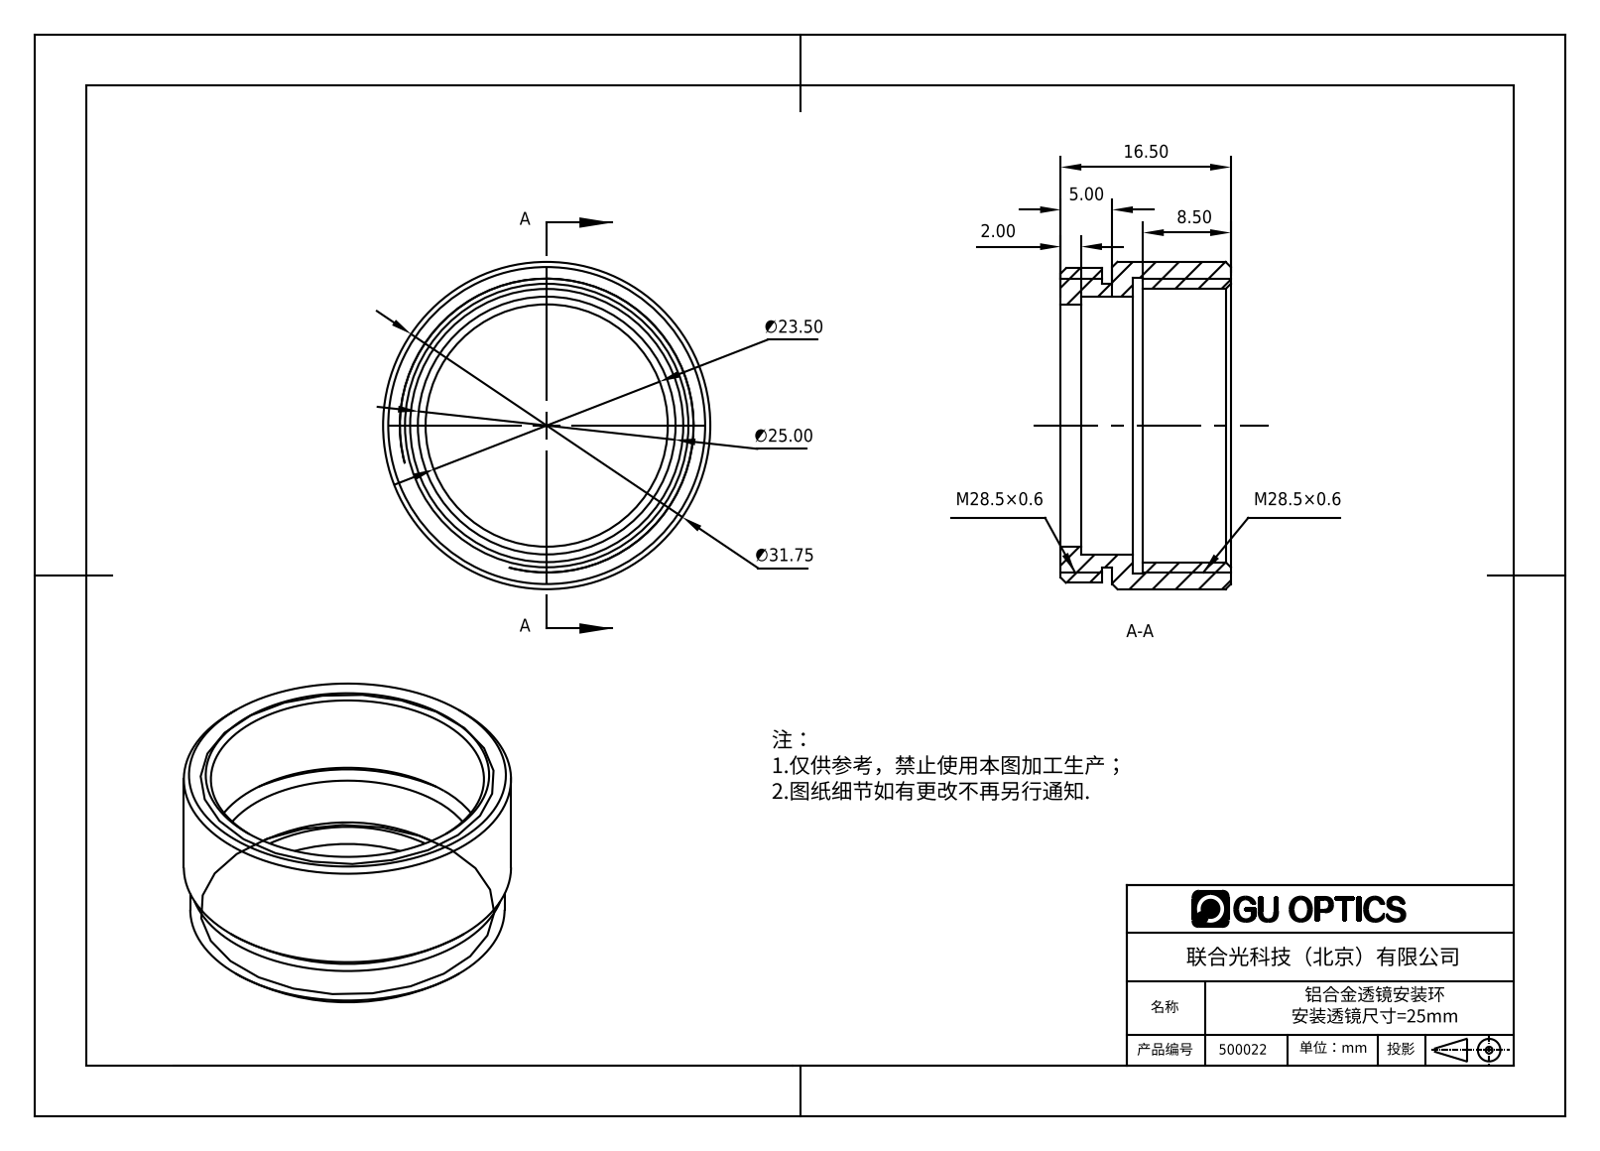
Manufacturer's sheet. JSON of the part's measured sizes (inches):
{"part_name": "500022", "step_written_by": "SolidWorks 2016 (AUTOMOTIVE_DESIGN)", "units": "inches", "bodies": {"solids": 1, "faces": 29, "planar": 7, "cylindrical": 14, "other": 8}, "overall_size": [1.25, 1.25, 0.65], "volume_in3": 0.239, "surface_area_in2": 6.236, "round_holes": [[0.925, 1], [0.984, 1], [1.043, 1], [1.13, 1]], "round_bosses_or_shafts": [[1.25, 1], [1.201, 1], [1.083, 1]], "face_to_face_distances": [0.118, 0.079, 0.157, 0.039, 0.197, 0.276, 0.65, 0.453, 0.374, 0.492]}
